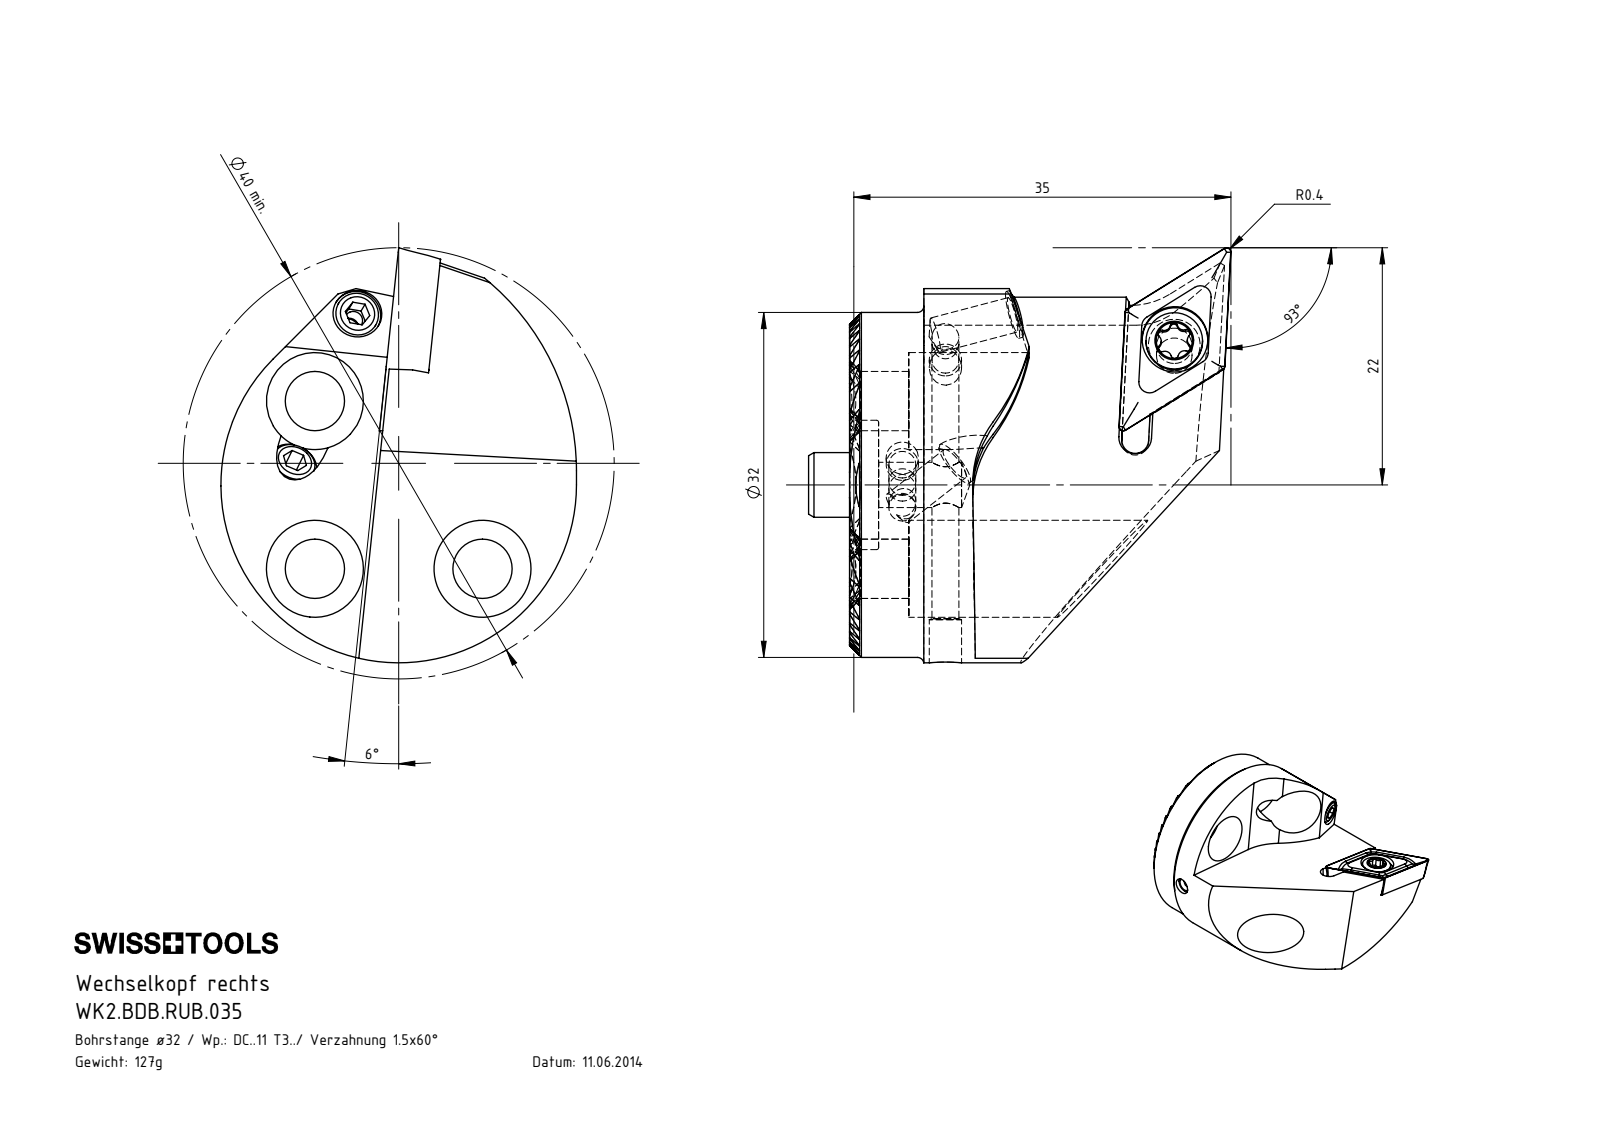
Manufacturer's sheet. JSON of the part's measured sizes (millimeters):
{"part_name": "WK2.BDB.RUB.035; WK2-ER1.001.012_A_Fertigbearbeitung; WCB-ER2.001.009_A; WKX-ER1.004.005_A_PreviewCfg (+3 more)", "step_written_by": "SolidWorks 2017 (AUTOMOTIVE_DESIGN)", "units": "millimeters", "bodies": {"solids": 12, "faces": 400, "planar": 197, "cylindrical": 102, "other": 101}, "overall_size": [39.2, 38.51, 33], "volume_mm3": 15899, "surface_area_mm2": 8312, "round_holes": [[2.38, 3], [2.5, 3], [3.3, 3], [5.5, 3], [9, 3], [1.7, 2], [3, 2], [4.5, 2], [4.2, 1], [4.4, 1], [6.1, 1], [12, 1]], "round_bosses_or_shafts": [[4, 3], [3, 3], [32, 1], [6, 1], [5.25, 1]], "partial_cylinders_radius": [[0.12, 22], [0.34, 6], [0.59, 6], [1.25, 1], [7, 1], [10, 1], [16.5, 1], [20, 1]], "face_to_face_distances": [1.3, 2.6, 3.9, 5.2, 6.5, 12.99, 11.69, 14.29, 7.8, 10.39], "hole_center_spacings": [11, 15.56, 22.01]}
